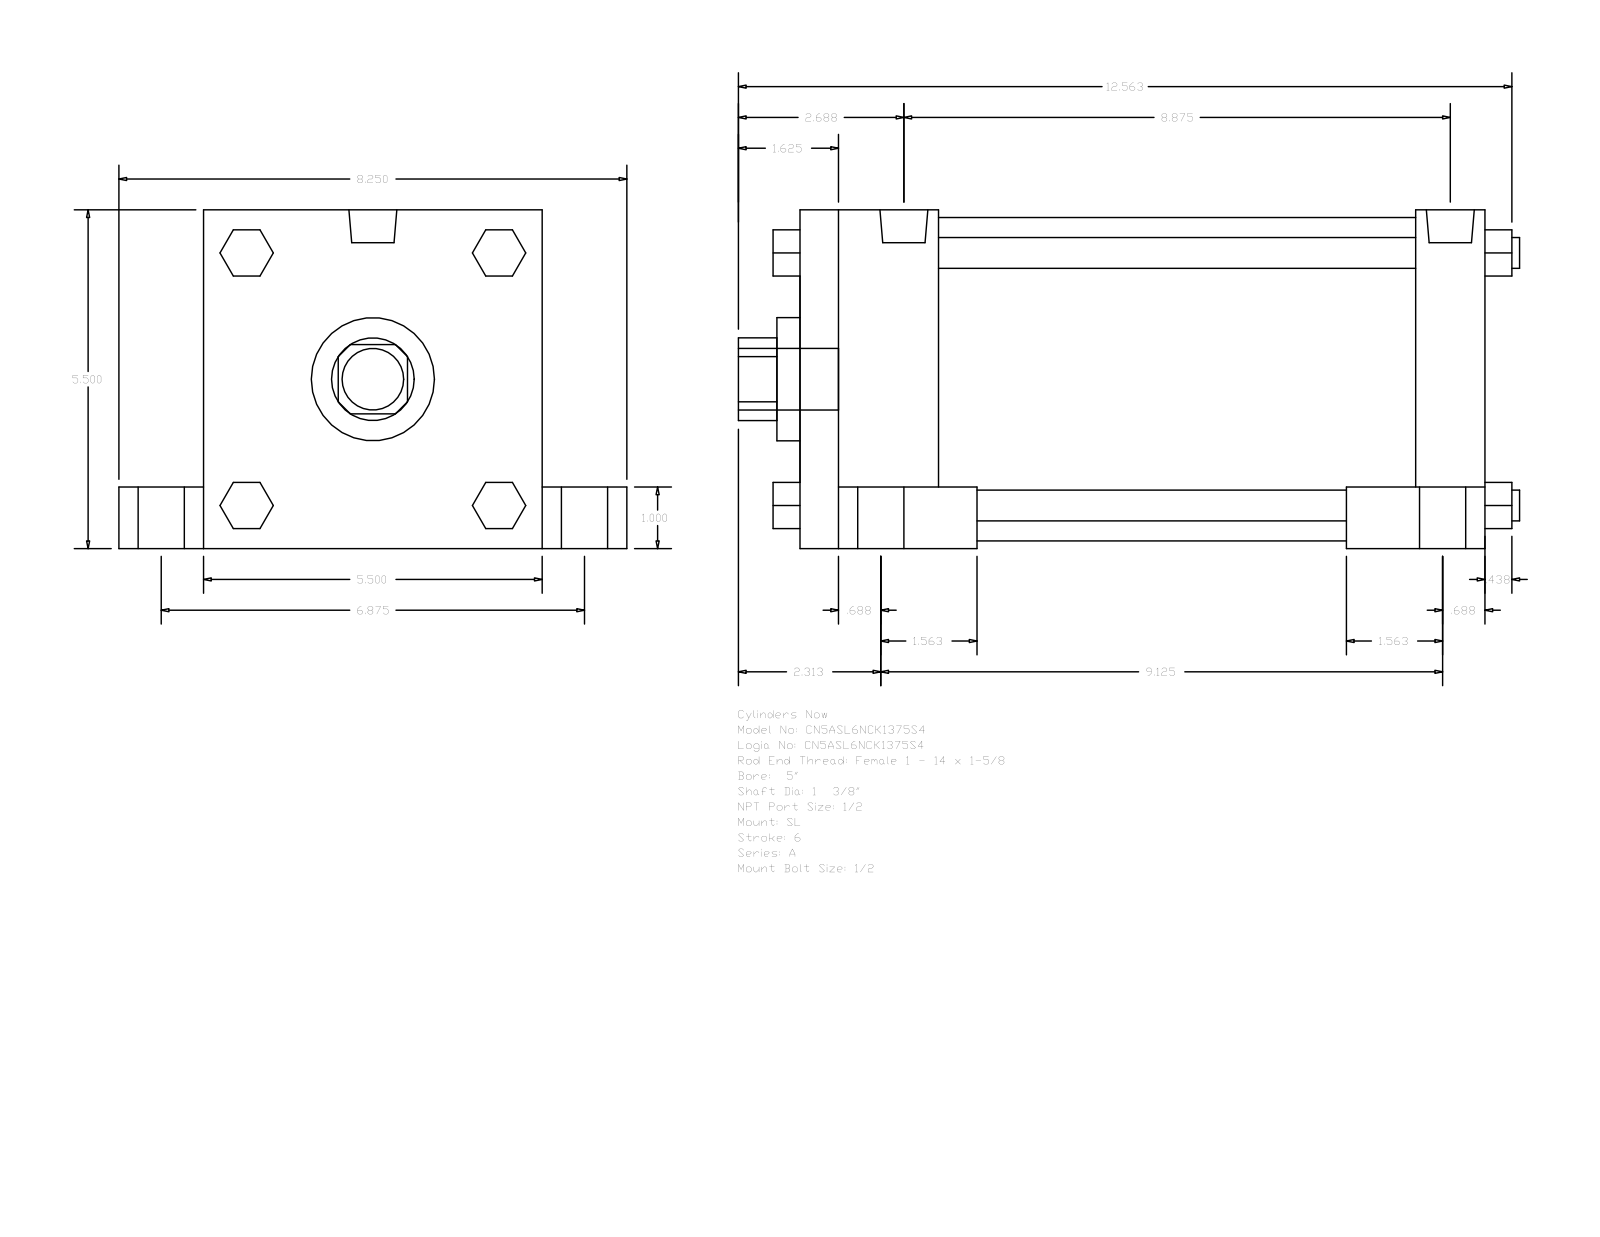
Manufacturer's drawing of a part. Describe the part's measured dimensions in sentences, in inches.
The part is named "A_SL__0500_1.375". Its 3-D file was written by "GSSL Pune (CONFIG_CONTROL_DESIGN)". It is 0 solids with 150 faces: 114 planar, 36 cylindrical and 0 other. Overall it measures 12.687 by 8.25 by 5.5 inches. Round holes: 1 of diameter 1.375, 1 of diameter 2, 1 of diameter 5.25. Round bosses or shafts: 5 of diameter 1, 4 of diameter 0.75, 4 of diameter 0.5, 4 of diameter 0.344, 2 of diameter 0.778. Partial cylindrical surfaces (rounded edges, fillets, slot ends): 1 of radius 0.672. The main face-to-face distances are 5.5, 11.125, 1.125, 2.25, 1, 4.5, 1.375, 6.875, 10, 7.75.
